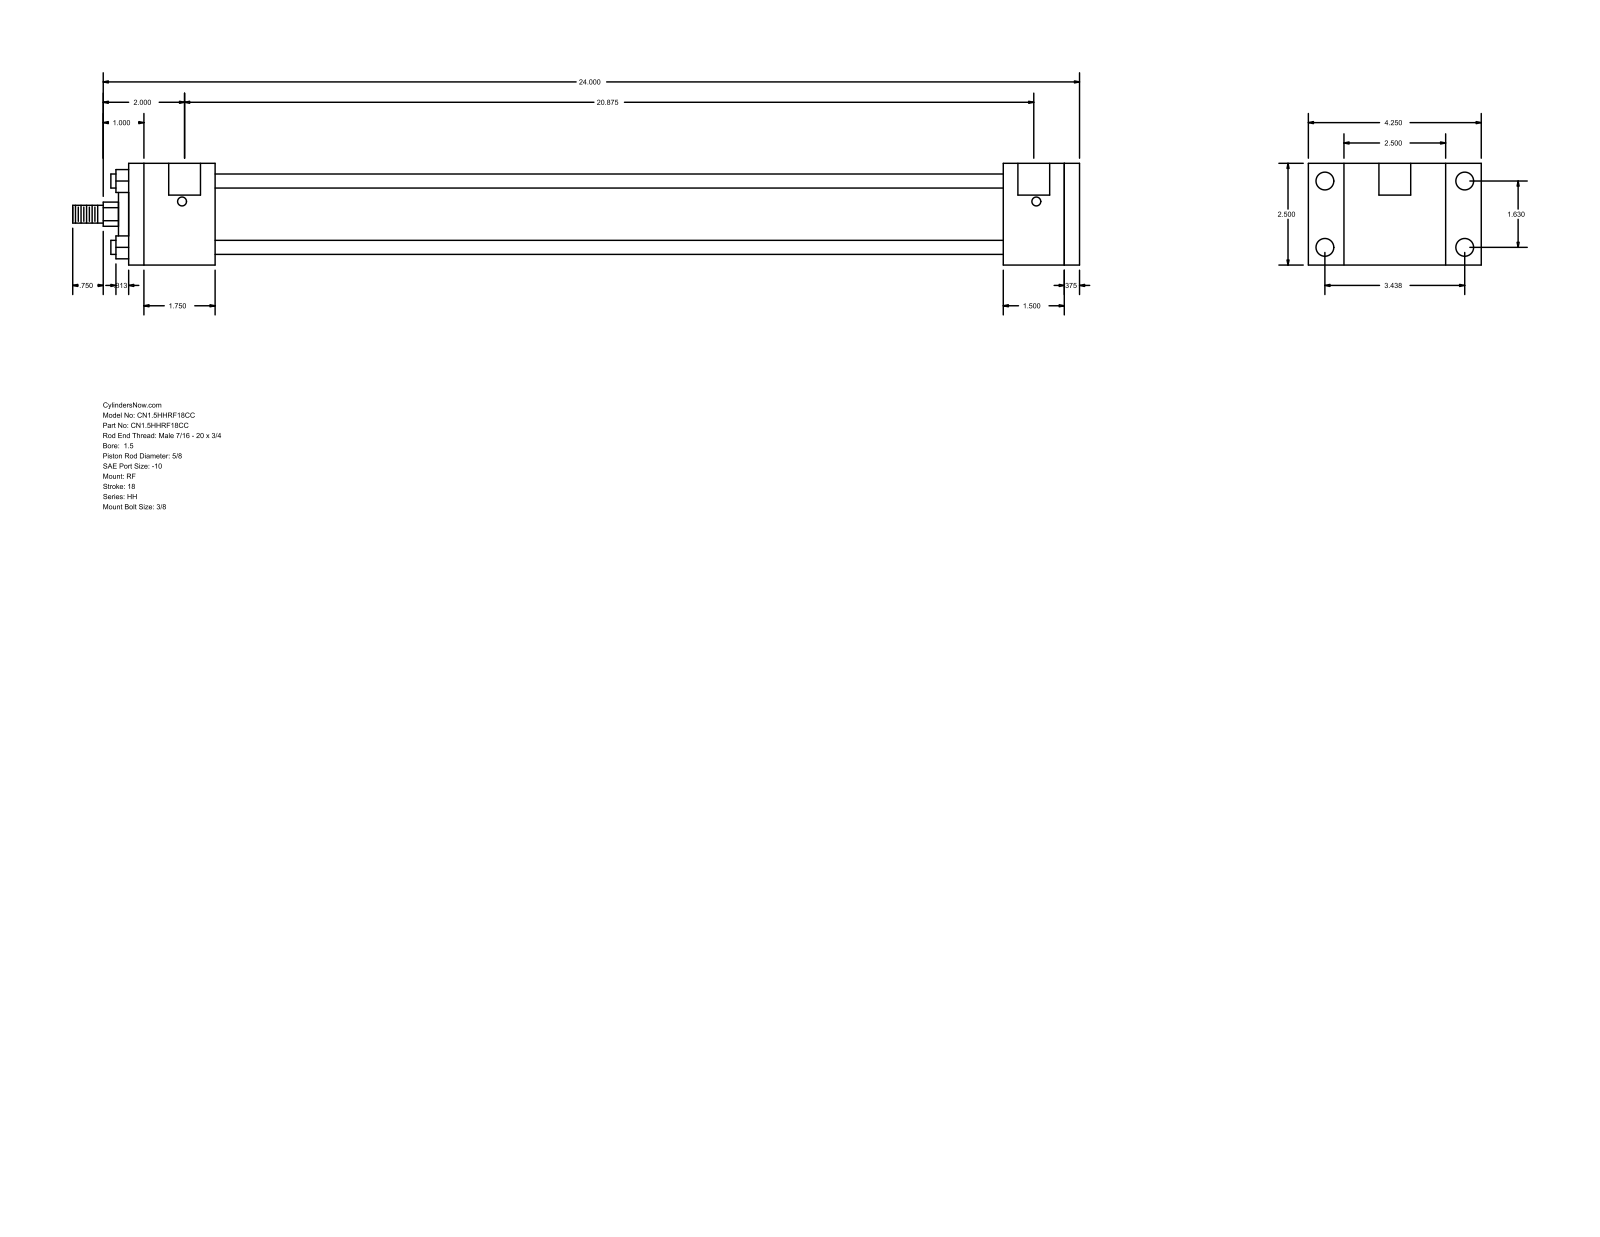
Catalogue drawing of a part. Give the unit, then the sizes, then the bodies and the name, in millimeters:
Units: millimetres
Overall size (bounding box): 628.65 × 107.95 × 63.5
Round holes (diameter × count): ⌀5.56 ×4, ⌀11.13 ×4, ⌀19.84 ×2
Round bosses / shafts (diameter × count): ⌀8.76 ×4, ⌀44.45 ×1, ⌀28.57 ×1, ⌀15.88 ×1, ⌀11.11 ×1
Partial cylindrical surfaces — rounded edges, fillets, slot ends (radius × count): R7.54 ×1
Main face-to-face distances: 63.5, 593.72, 38.1, 584.2, 9.52, 53.97, 546.1, 492.13, 530.23, 539.75
Hole centre spacings: 1.59, 41.4, 87.32, 96.64, 531.81, 533.4, 530.22
Bodies: 0 solids, 92 faces (64 planar, 28 cylindrical, 0 other)
Part name (STEP PRODUCT): HH_RF__0150_0.625
STEP written by: GSSL Pune (CONFIG_CONTROL_DESIGN)
